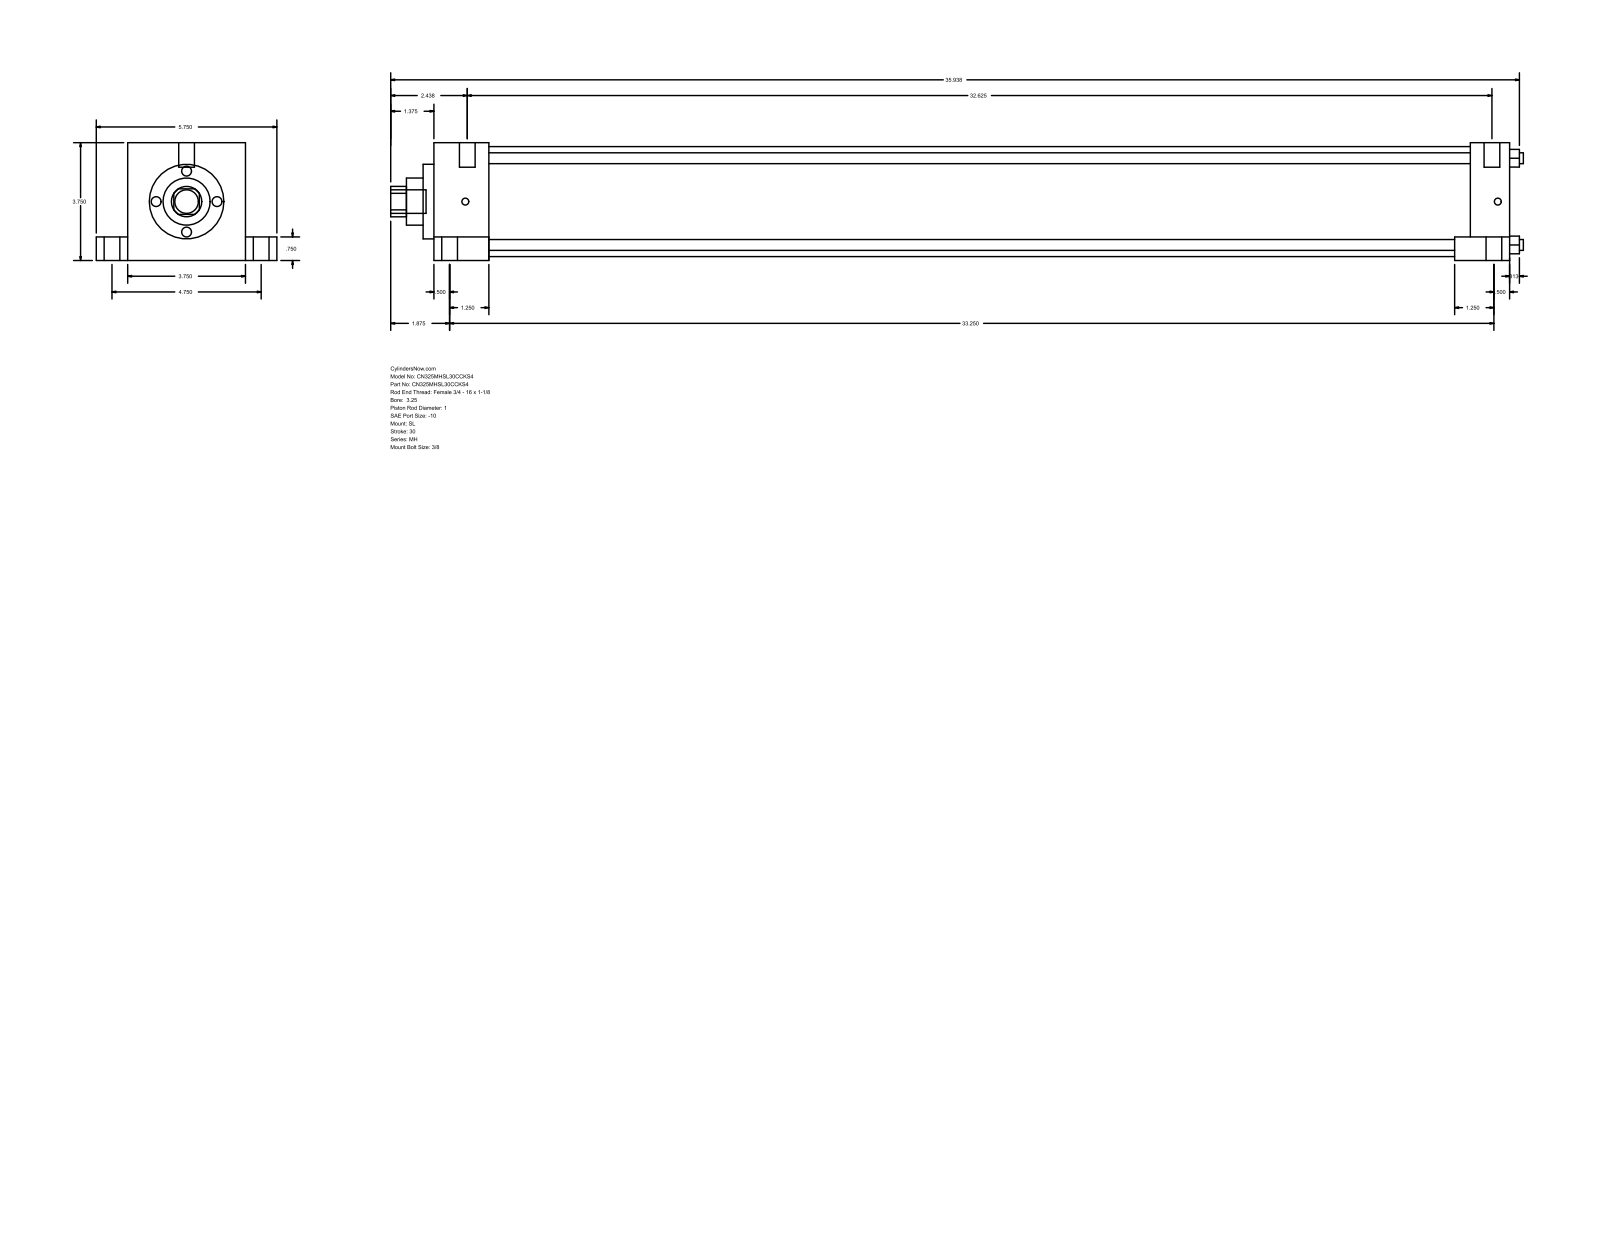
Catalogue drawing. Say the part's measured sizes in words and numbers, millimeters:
The part is named "MH_SL__0325_1". Its 3-D file was written by "GSSL Pune (CONFIG_CONTROL_DESIGN)". It is 0 solids with 110 faces: 77 planar, 33 cylindrical and 0 other. Overall it measures 915.99 by 146.05 by 95.25 millimeters. Round holes: 4 of diameter 8.76, 1 of diameter 25.4, 1 of diameter 38.1, 1 of diameter 60.33, 1 of diameter 88.9. Round bosses or shafts: 6 of diameter 12.7, 5 of diameter 19.05, 4 of diameter 5.56. Partial cylindrical surfaces (rounded edges, fillets, slot ends): 1 of radius 12.29. The main face-to-face distances are 95.24, 869.96, 44.46, 825.5, 25.41, 120.65, 19.05, 76.19, 838.2, 793.74. The hole center spacings are 49.57, 70.1, 99.14.
